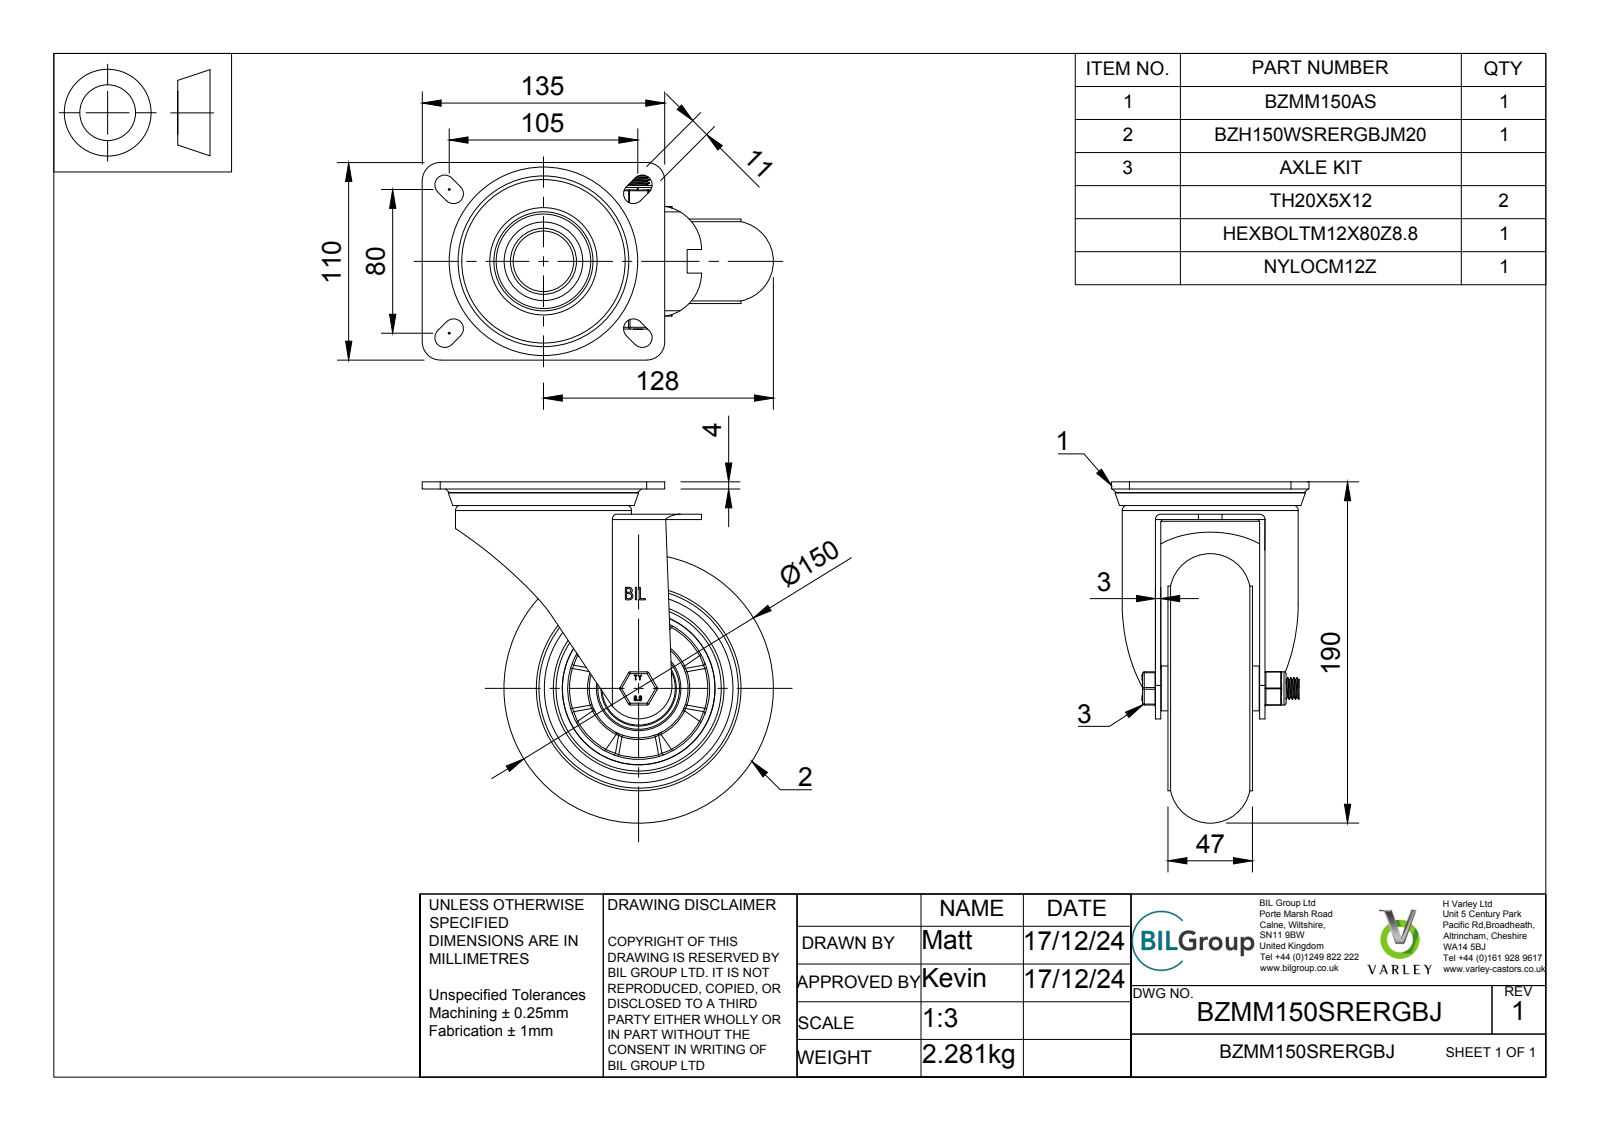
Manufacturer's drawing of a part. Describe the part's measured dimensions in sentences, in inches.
The part is named "BZMM150SRERGBJ v3; BZMM150AS - 2 - 55 v1; ZINC PLATED, PRESSED STEEL TOP PLATE; ZINC PLATED, PRESSED STEEL TOP PLATE Geometry (+7 more)". Its 3-D file was written by "Autodesk Translation Framework v13.20.0.188 (AP242_MANAGED_MODEL_BASED_3D_ENGINEERING_MIM_LF)". It is 77 solids with 1271 faces: 439 planar, 213 cylindrical and 619 other. Overall it measures 7.697 by 7.48 by 4.331 inches. Its volume is 44.75 cubic inches and its surface area 385.2 square inches. Round holes: 2 of diameter 3.622, 1 of diameter 0.472, 1 of diameter 0.48, 1 of diameter 0.492, 1 of diameter 0.551, 1 of diameter 0.787, 1 of diameter 1.122, 1 of diameter 1.213, 1 of diameter 1.329, 1 of diameter 1.565, 1 of diameter 1.587, 1 of diameter 1.594. Round bosses or shafts: 1 of diameter 4.488, 1 of diameter 3.858, 1 of diameter 3.74, 1 of diameter 3.071, 1 of diameter 2.165, 1 of diameter 1.969, 1 of diameter 1.606, 1 of diameter 1.232. Partial cylindrical surfaces (rounded edges, fillets, slot ends): 18 of radius 0.02, 12 of radius 0.039, 8 of radius 0.217, 4 of radius 0.059, 4 of radius 0.394, 2 of radius 0.118, 2 of radius 0.957, 1 of radius 0.65. The main face-to-face distances are 0.118, 0.354, 0.197, 0.157, 0.551, 0.315, 0.472, 0.63, 0.079, 2.283.
